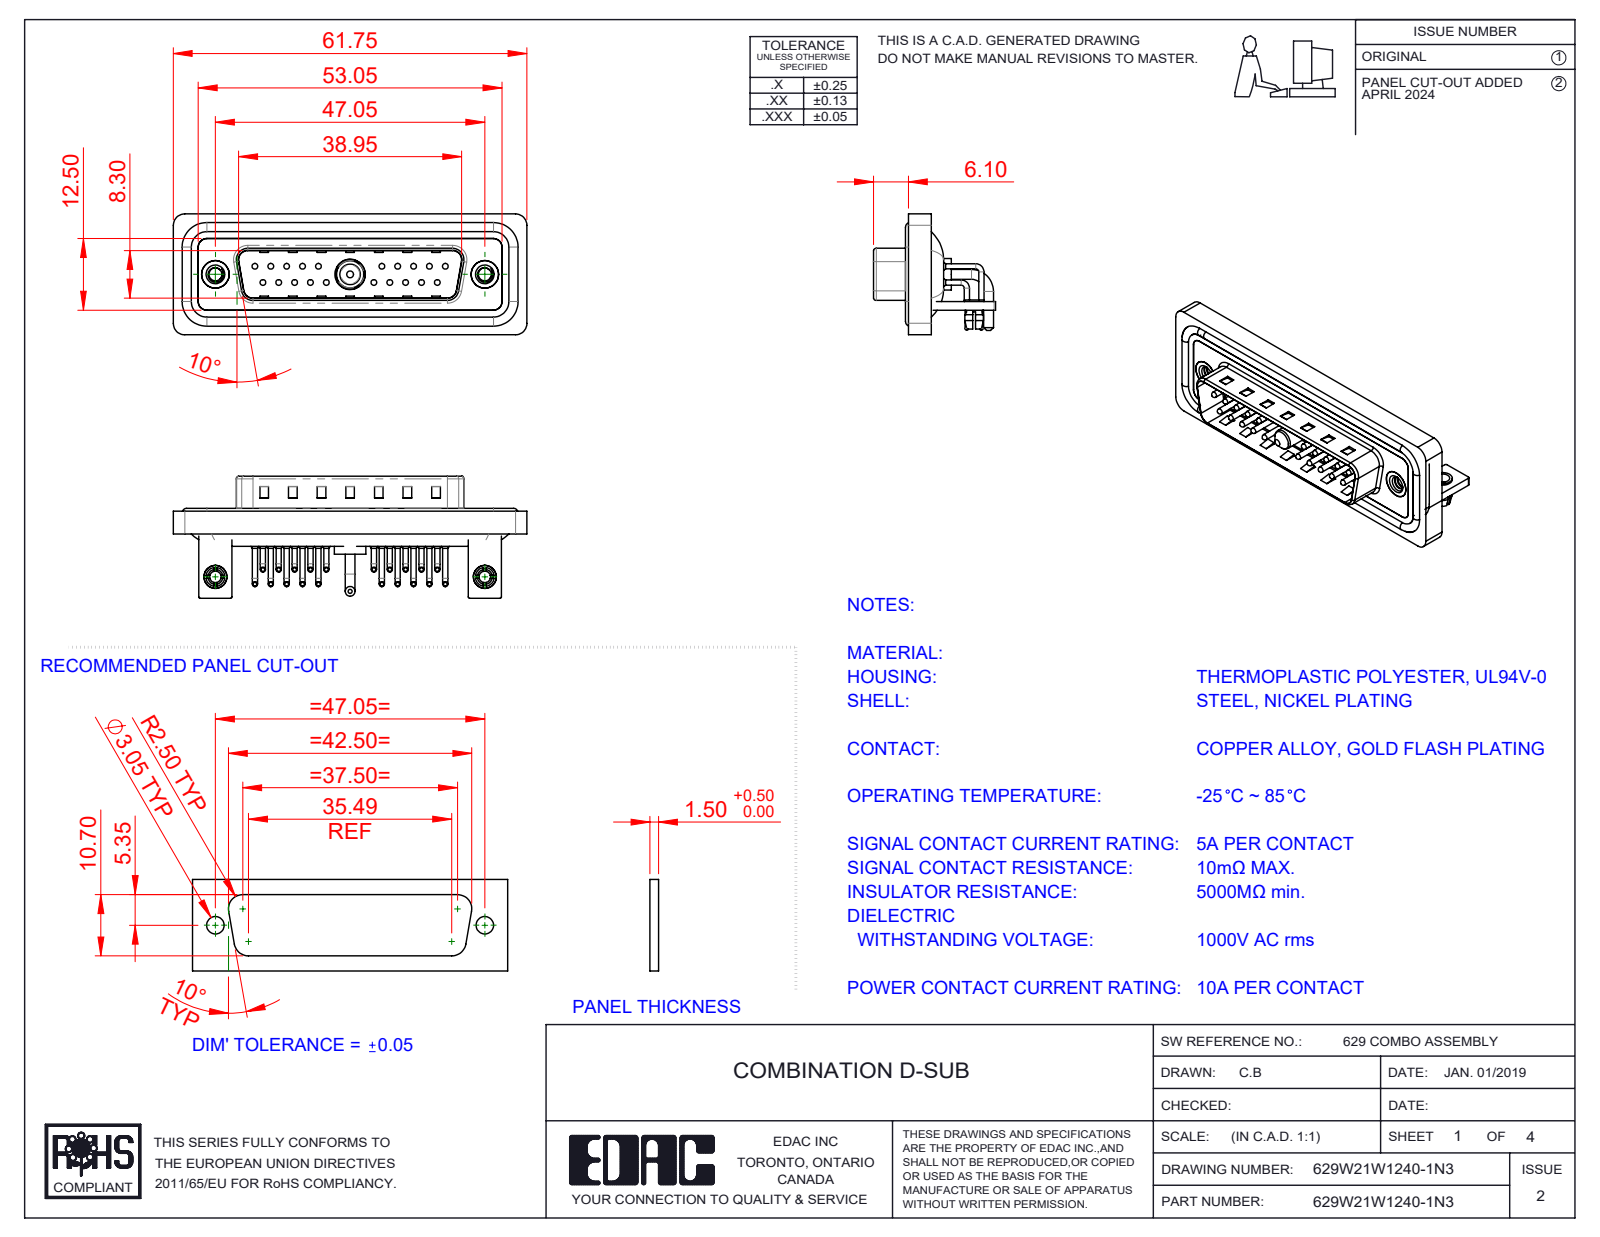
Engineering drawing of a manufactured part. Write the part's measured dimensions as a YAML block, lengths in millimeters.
part_name: "629Combo Threaded Rivet_3; 629Combo Shell Rear_25 Contacts; Power Pin_10A RA; 629W21W1240-1N3 (+7 more)"
step_written_by: "SolidWorks 2023 (CONFIG_CONTROL_DESIGN)"
units: millimeters
bodies: {solids: 33, faces: 2858, planar: 1567, cylindrical: 979, other: 312}
overall_size: [61.75, 21.3, 21.1]
volume: 7674
surface_area: 13467
round_holes:
  - {diameter: 2, count: 22}
  - {diameter: 0.75, count: 20}
  - {diameter: 1.6, count: 20}
  - {diameter: 2.26, count: 2}
  - {diameter: 2.5, count: 2}
  - {diameter: 3.2, count: 2}
  - {diameter: 4, count: 2}
  - {diameter: 4.8, count: 2}
  - {diameter: 5, count: 2}
  - {diameter: 4.85, count: 1}
  - {diameter: 5.3, count: 1}
round_bosses_or_shafts:
  - {diameter: 0.9, count: 40}
  - {diameter: 1.5, count: 20}
  - {diameter: 1, count: 20}
  - {diameter: 0.65, count: 20}
  - {diameter: 1.6, count: 4}
  - {diameter: 4.9, count: 2}
  - {diameter: 4, count: 2}
  - {diameter: 3.4, count: 2}
partial_cylinders:
  - {radius: 1.01, count: 20}
  - {radius: 2, count: 19}
  - {radius: 1.5, count: 18}
  - {radius: 0.25, count: 16}
  - {radius: 0.5, count: 9}
  - {radius: 1.6, count: 8}
  - {radius: 0.6, count: 4}
  - {radius: 0.65, count: 4}
face_to_face_distances: [0.4, 0.8, 2.1, 2.9, 1.5, 1.1, 4.1, 1.6, 4.5, 3.7]
hole_center_spacings: [3.16, 2.77, 5.54, 8.31, 5.04, 19.39, 20.97, 22.16]
